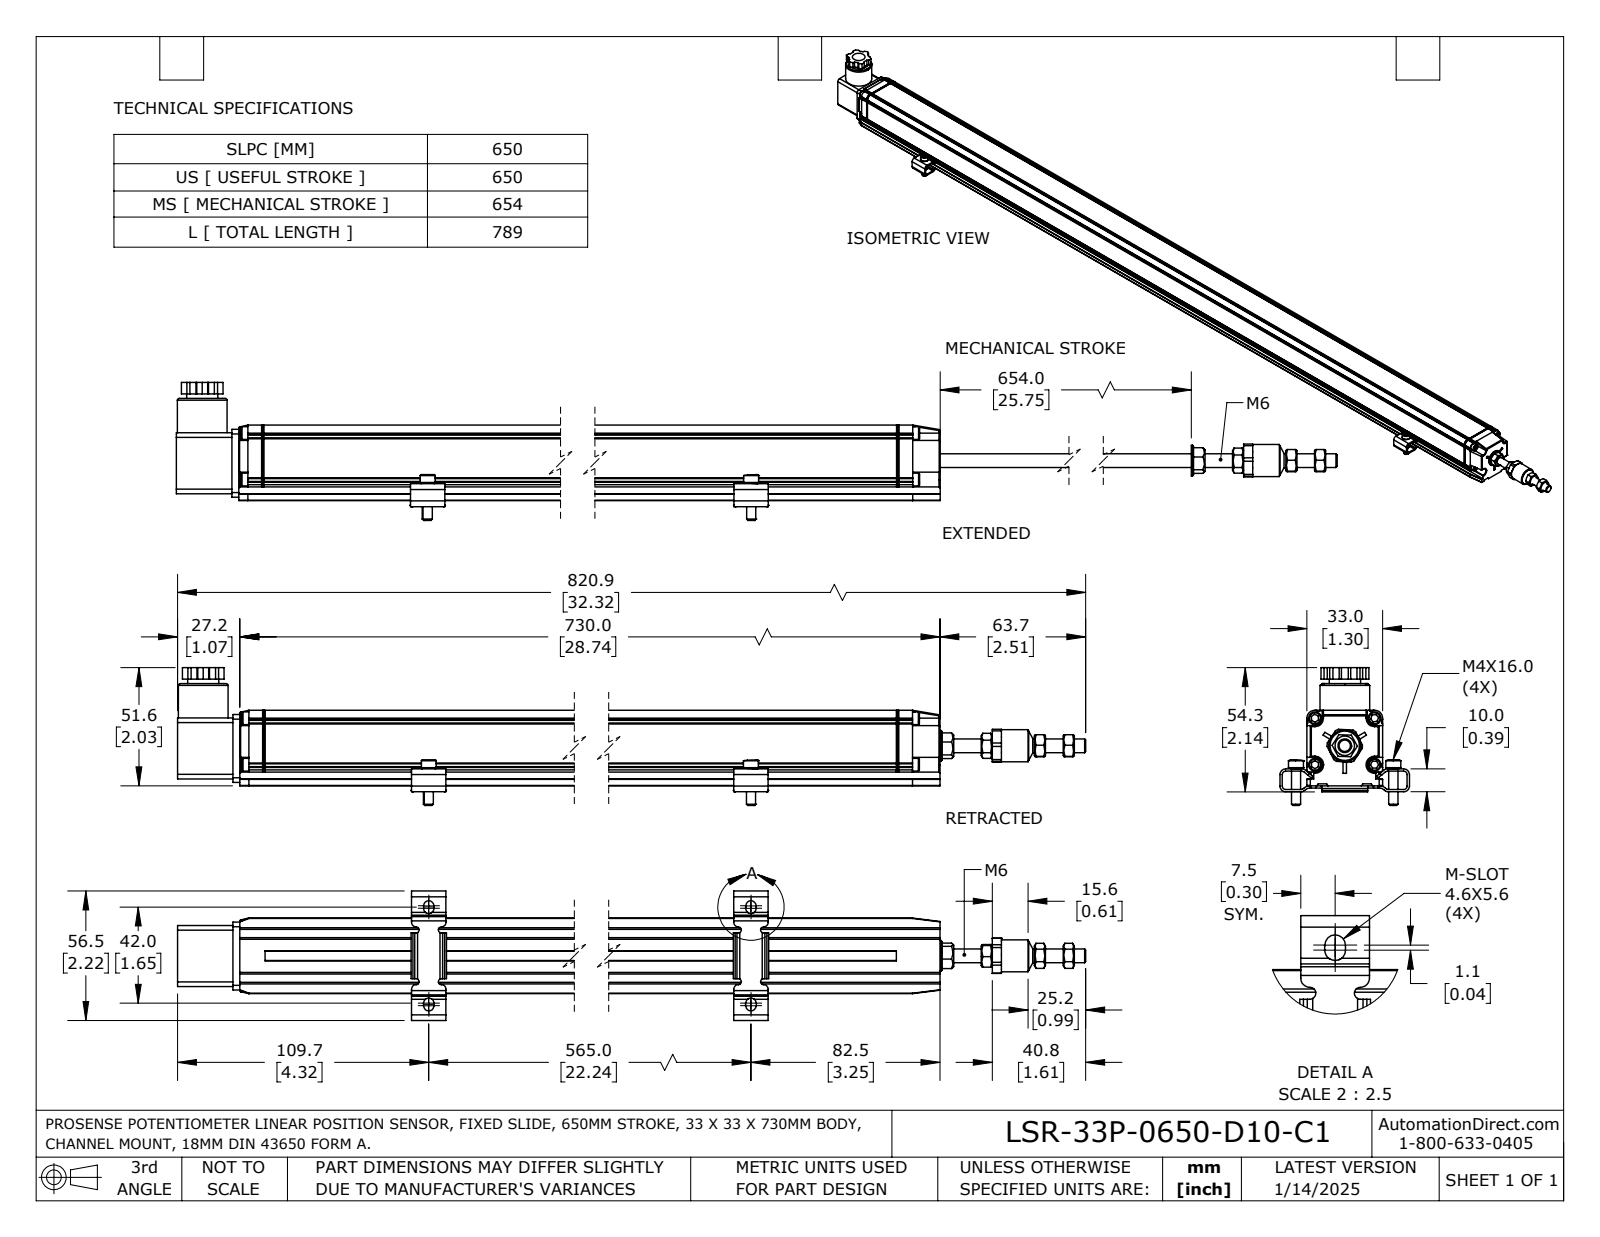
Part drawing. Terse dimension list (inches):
name: LSR-33P-0650-D10-C1
written by: SolidWorks 2023 (AUTOMOTIVE_DESIGN)
unit: in
bodies: 14 solids, 995 faces (641 planar, 269 cylindrical, 85 other)
size: 32.317 × 2.37 × 2.224
volume: 44.8 in³; area: 273 in²
holes: 4× ⌀0.106, 4× ⌀0.13, 1× ⌀0.169, 1× ⌀0.205, 1× ⌀0.209, 1× ⌀0.232, 1× ⌀0.276, 1× ⌀0.285, 1× ⌀0.394, 1× ⌀0.413, 1× ⌀0.573, 1× ⌀0.602
bosses: 5× ⌀0.157, 5× ⌀0.118, 4× ⌀0.256, 4× ⌀0.22, 1× ⌀0.854, 1× ⌀0.551, 1× ⌀0.535, 1× ⌀0.528
rounds: 28× R0.079, 23× R0.02, 16× R0.008, 8× R0.051, 8× R0.059, 8× R0.089, 8× R0.118, 4× R0.039
face distances: 1.299, 0.118, 0.22, 1.181, 1.079, 0.039, 0.079, 0.142, 1.22, 0.185
hole spacings: 0.047, 0.583, 0.607, 0.696, 0.73, 0.799, 1.024, 1.299
